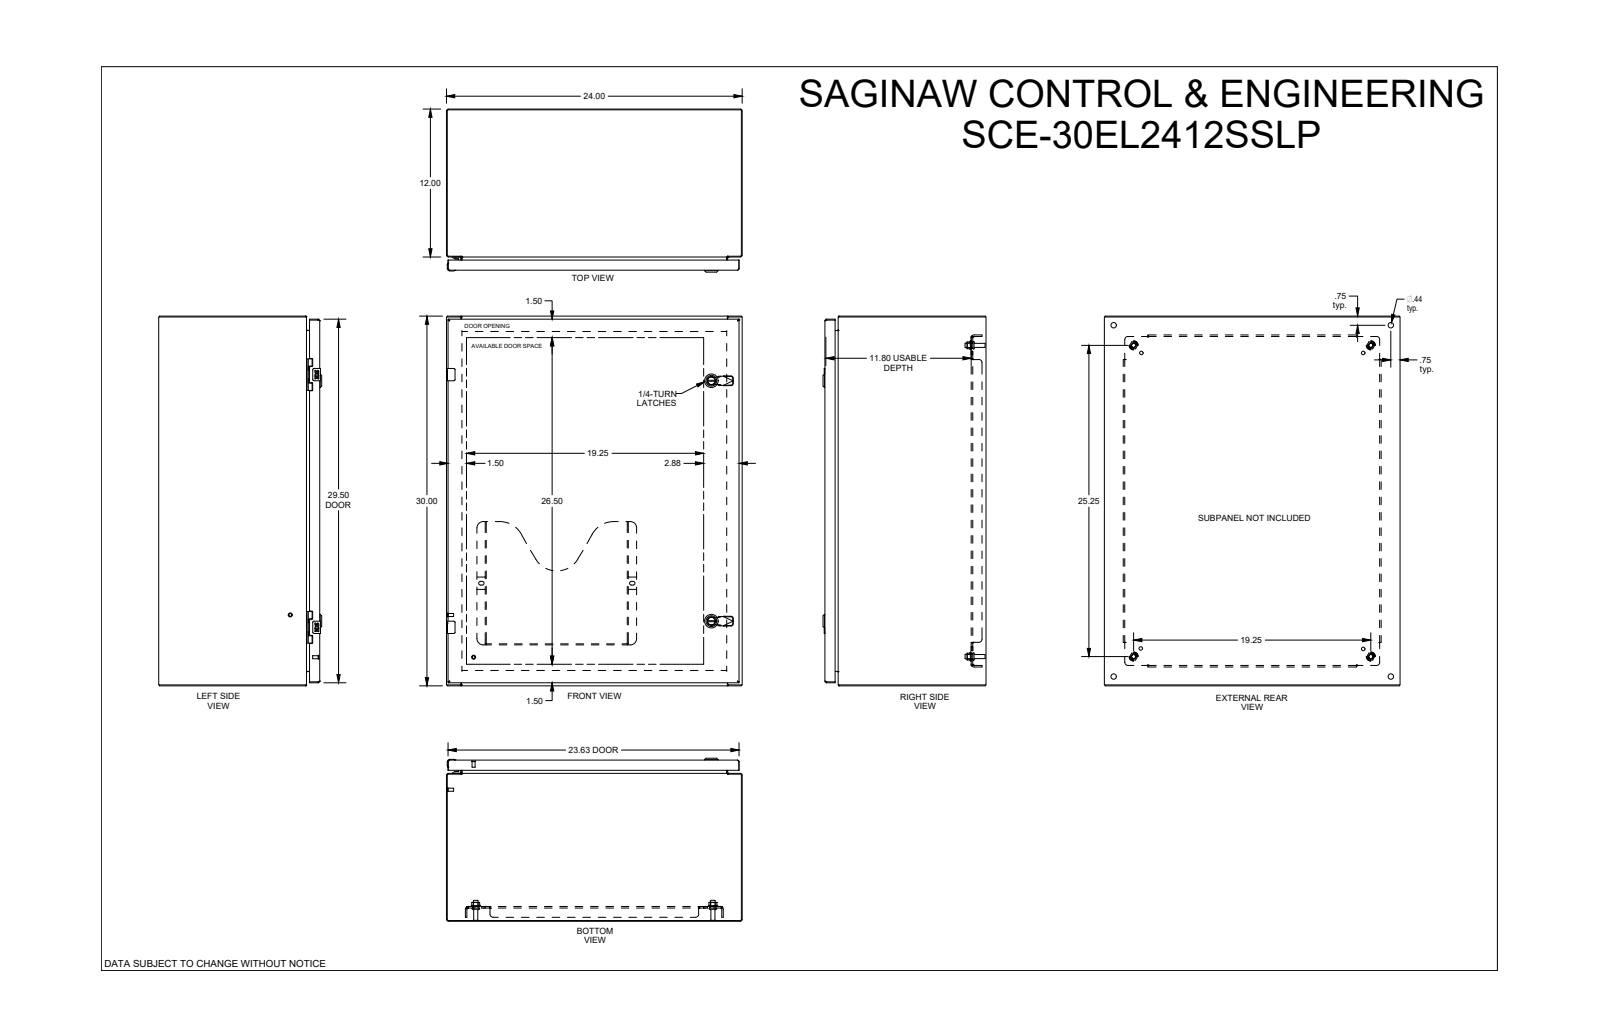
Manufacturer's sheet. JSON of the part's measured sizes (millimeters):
{"part_name": "SCE-30EL2412SSLP", "step_written_by": "SolidWorks 2019 (CONFIG_CONTROL_DESIGN)", "units": "millimeters", "bodies": {"solids": 0, "faces": 2838, "planar": 1307, "cylindrical": 759, "other": 772}, "overall_size": [762, 609.6, 336], "round_holes": [[4.4, 4], [5.2, 4], [6.2, 4], [6.8, 4], [7.1, 4], [9.3, 4], [11.1, 4], [12.7, 4], [9.5, 3], [4, 2], [5, 2], [5.5, 2]], "round_bosses_or_shafts": [[4.3, 6], [9.3, 4], [8.4, 4], [6.4, 4], [6.3, 4], [5, 3], [28, 2], [22, 2]], "partial_cylinders_radius": [[0.3, 56], [0.4, 32], [0.3, 28], [1, 23], [0.5, 20], [0.7, 12], [1.8, 10], [3.7, 10]], "face_to_face_distances": [1.9, 1.9, 328.2, 330.1, 607.7, 332.1, 330.1, 30.5, 301.6, 25.4], "hole_center_spacings": [520.7, 25, 0.5, 22.2, 114.1, 531.8, 80.6, 473.5]}
